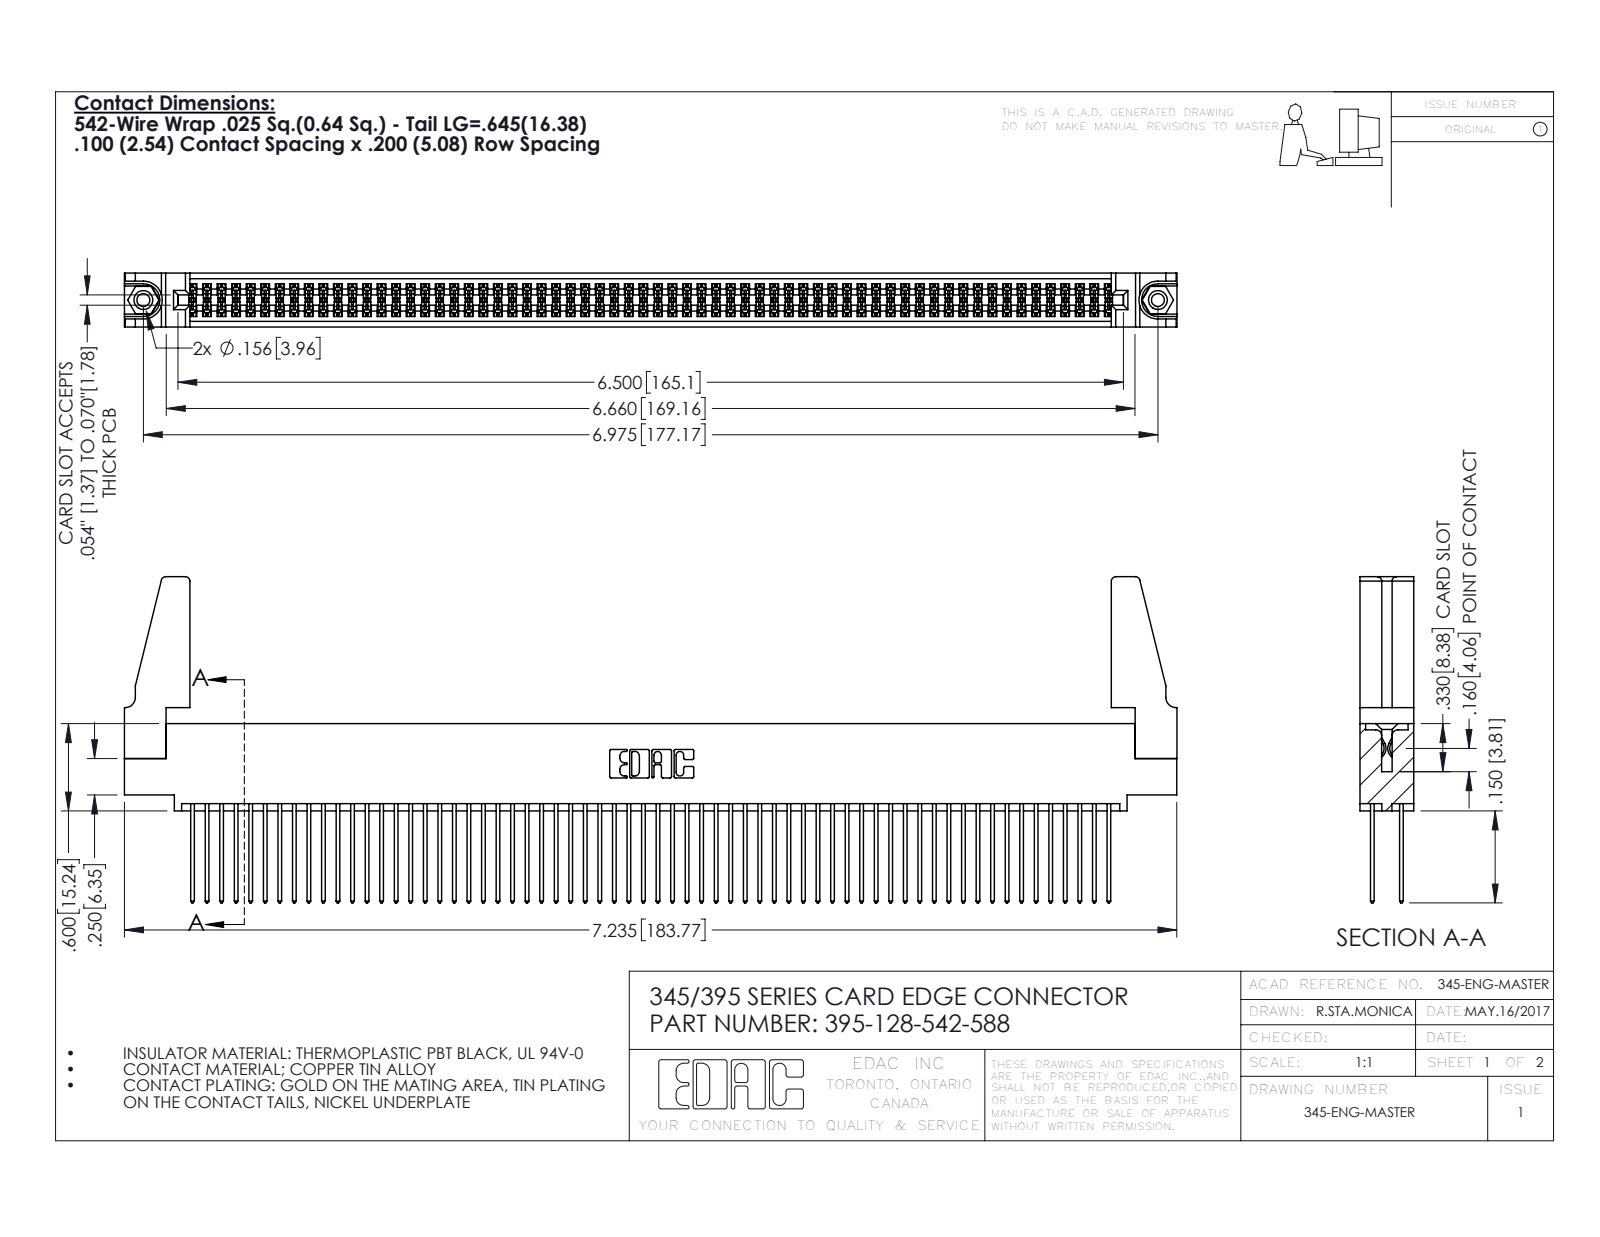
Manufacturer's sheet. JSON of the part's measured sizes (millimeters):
{"part_name": "395-128-542-588; 345-220-078_345-220-088; 345-292-001_345-293-142; 345-250-001_345-250-001-102 (+1 more)", "step_written_by": "SolidWorks 2016 (CONFIG_CONTROL_DESIGN)", "units": "millimeters", "bodies": {"solids": 133, "faces": 6654, "planar": 4380, "cylindrical": 2258, "other": 16}, "overall_size": [183.8, 56.9, 9.4], "volume_mm3": 21830, "surface_area_mm2": 33900, "round_holes": [[2.3, 2], [3.2, 2], [4, 2], [1.6, 1]], "round_bosses_or_shafts": [[3.9, 2]], "partial_cylinders_radius": [[0.2, 192], [0.3, 128], [0.3, 22], [0.8, 8], [0.2, 6], [0.8, 6], [0.7, 3], [0.4, 2]], "face_to_face_distances": [1.8, 7.6, 2.5, 6.9, 0.6, 5.1, 9.4, 5.7, 4.4, 3.8], "hole_center_spacings": [6.9, 171.2, 177.2]}
